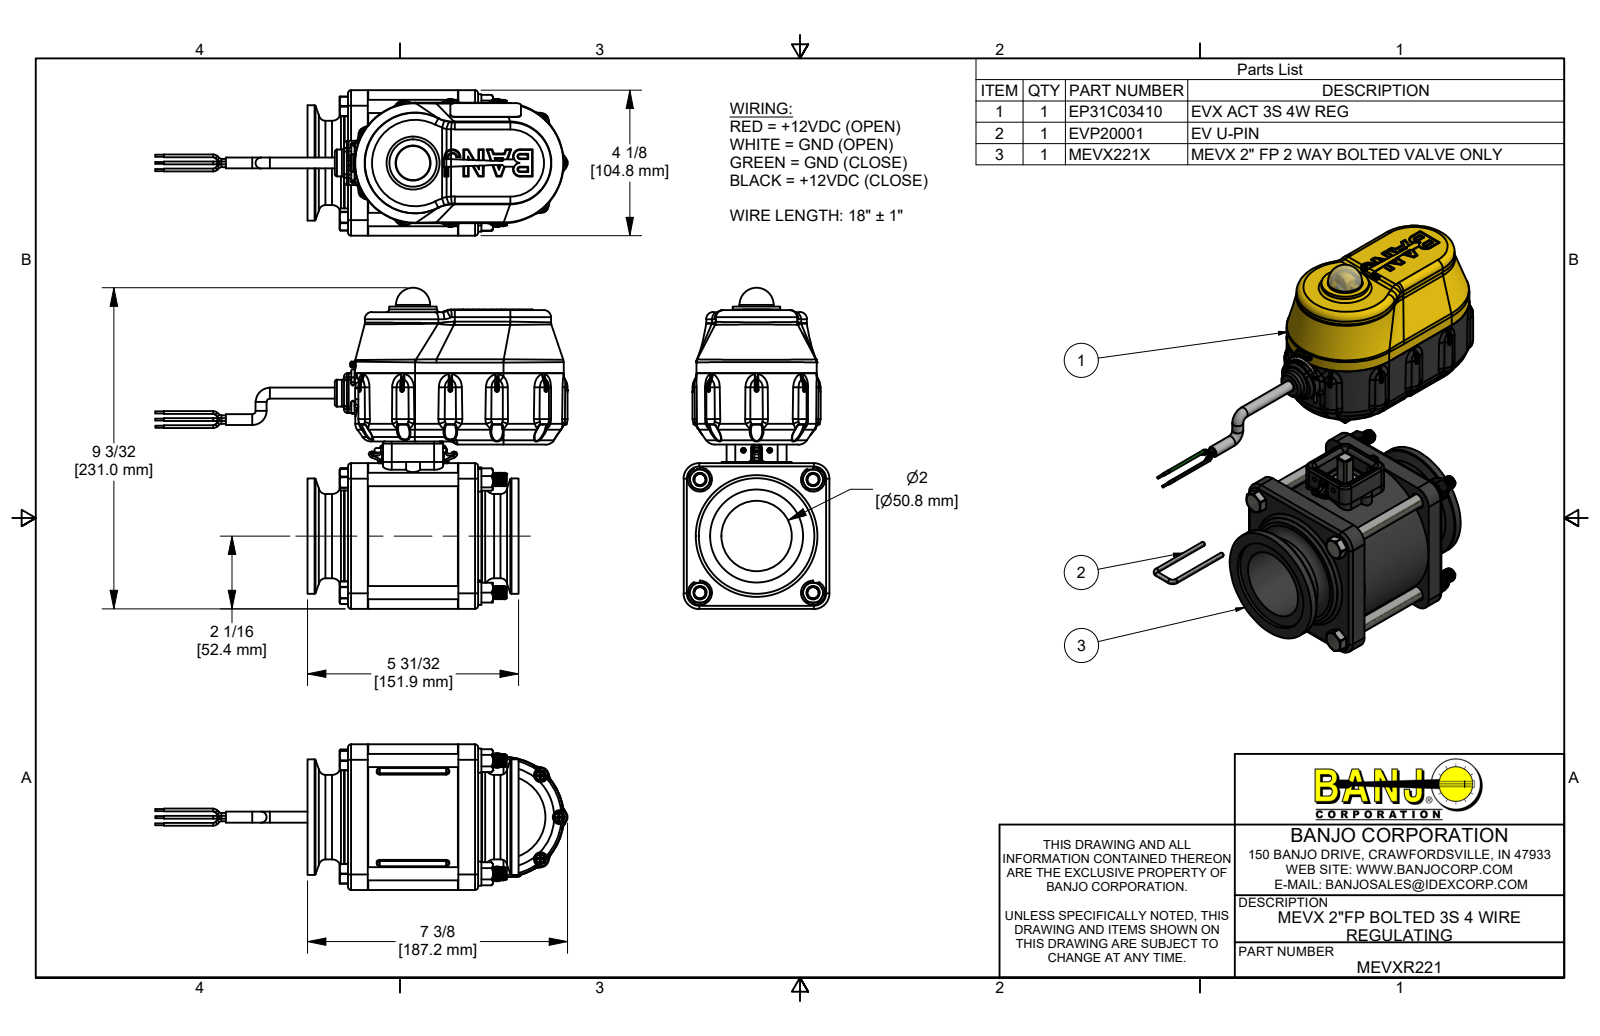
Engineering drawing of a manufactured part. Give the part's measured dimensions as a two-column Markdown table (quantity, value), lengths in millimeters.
| quantity | value |
| --- | --- |
| part name | MEVXR221; MEVX221X; MEVX25254A; MEVX25254AX (+8 more) |
| STEP written by | Autodesk Inventor 2021 (AUTOMOTIVE_DESIGN) |
| units | millimeters |
| bodies | 95 solids, 12515 faces (3540 planar, 3365 cylindrical, 5610 other) |
| overall size | 296.8 × 231 × 104.8 |
| volume | 1 171 000 mm³ |
| surface area | 479 000 mm² |
| round holes (diameter × count) | 3.8 × 13, 2.4 × 11, 2.7 × 4, 3.2 × 4, 3.5 × 4, 4.3 × 4, 7.8 × 4, 9.8 × 4, 11.7 × 4, 3.4 × 3, 2.3 × 2, 2.7 × 2 |
| round bosses / shafts (diameter × count) | 8.2 × 60, 2 × 20, 6.4 × 17, 3.6 × 11, 2.7 × 11, 2.2 × 11, 1.5 × 8, 9.5 × 5 |
| partial cylindrical surfaces (radius × count) | 1 × 147, 0.5 × 108, 0.3 × 58, 0.1 × 47, 0.8 × 43, 0.4 × 32, 1.5 × 28, 2 × 28 |
| main face-to-face distances | 2.5, 65.2, 16.4, 77.3, 63.8, 63.1, 2.2, 14.2, 79.5, 1.9 |
| hole center spacings | 57.5, 81.4, 42.2, 62.4, 69.3, 87.6, 107, 114 |
